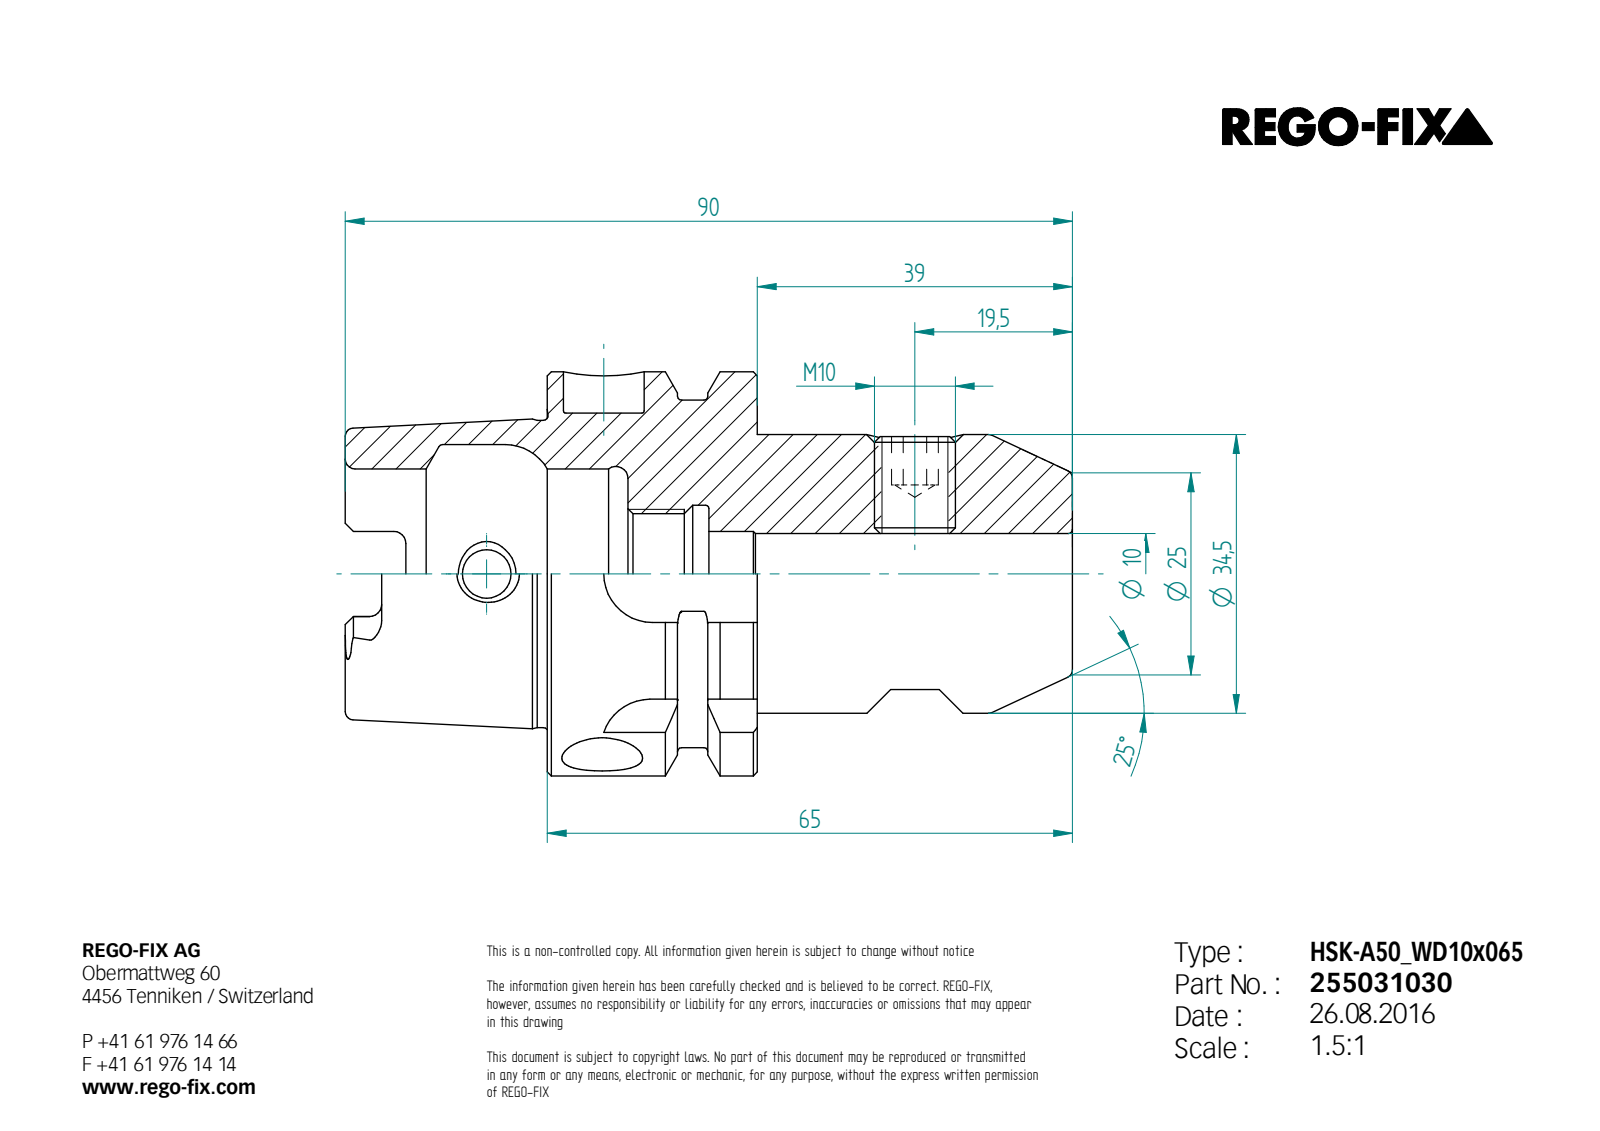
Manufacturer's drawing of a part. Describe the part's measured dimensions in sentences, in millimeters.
Its 3-D file was written by "Unknown (AUTOMOTIVE_DESIGN)". It is 3 solids with 156 faces: 64 planar, 37 cylindrical and 55 other. Overall it measures 90 by 50 by 50 millimeters. Its volume is 82 721 cubic millimeters and its surface area 22 613 square millimeters. Round holes: 3 of diameter 10, 1 of diameter 6, 1 of diameter 8.38, 1 of diameter 10.5, 1 of diameter 14.92, 1 of diameter 17, 1 of diameter 26, 1 of diameter 32. Round bosses or shafts: 1 of diameter 50, 1 of diameter 43, 1 of diameter 38.01, 1 of diameter 34.5, 1 of diameter 10. Partial cylindrical surfaces (rounded edges, fillets, slot ends): 6 of radius 1.5, 4 of radius 2.38, 4 of radius 6. The main face-to-face distances are 26, 65, 39, 10, 45, 16, 55, 42, 25, 35. The hole center spacings are 38.5.
